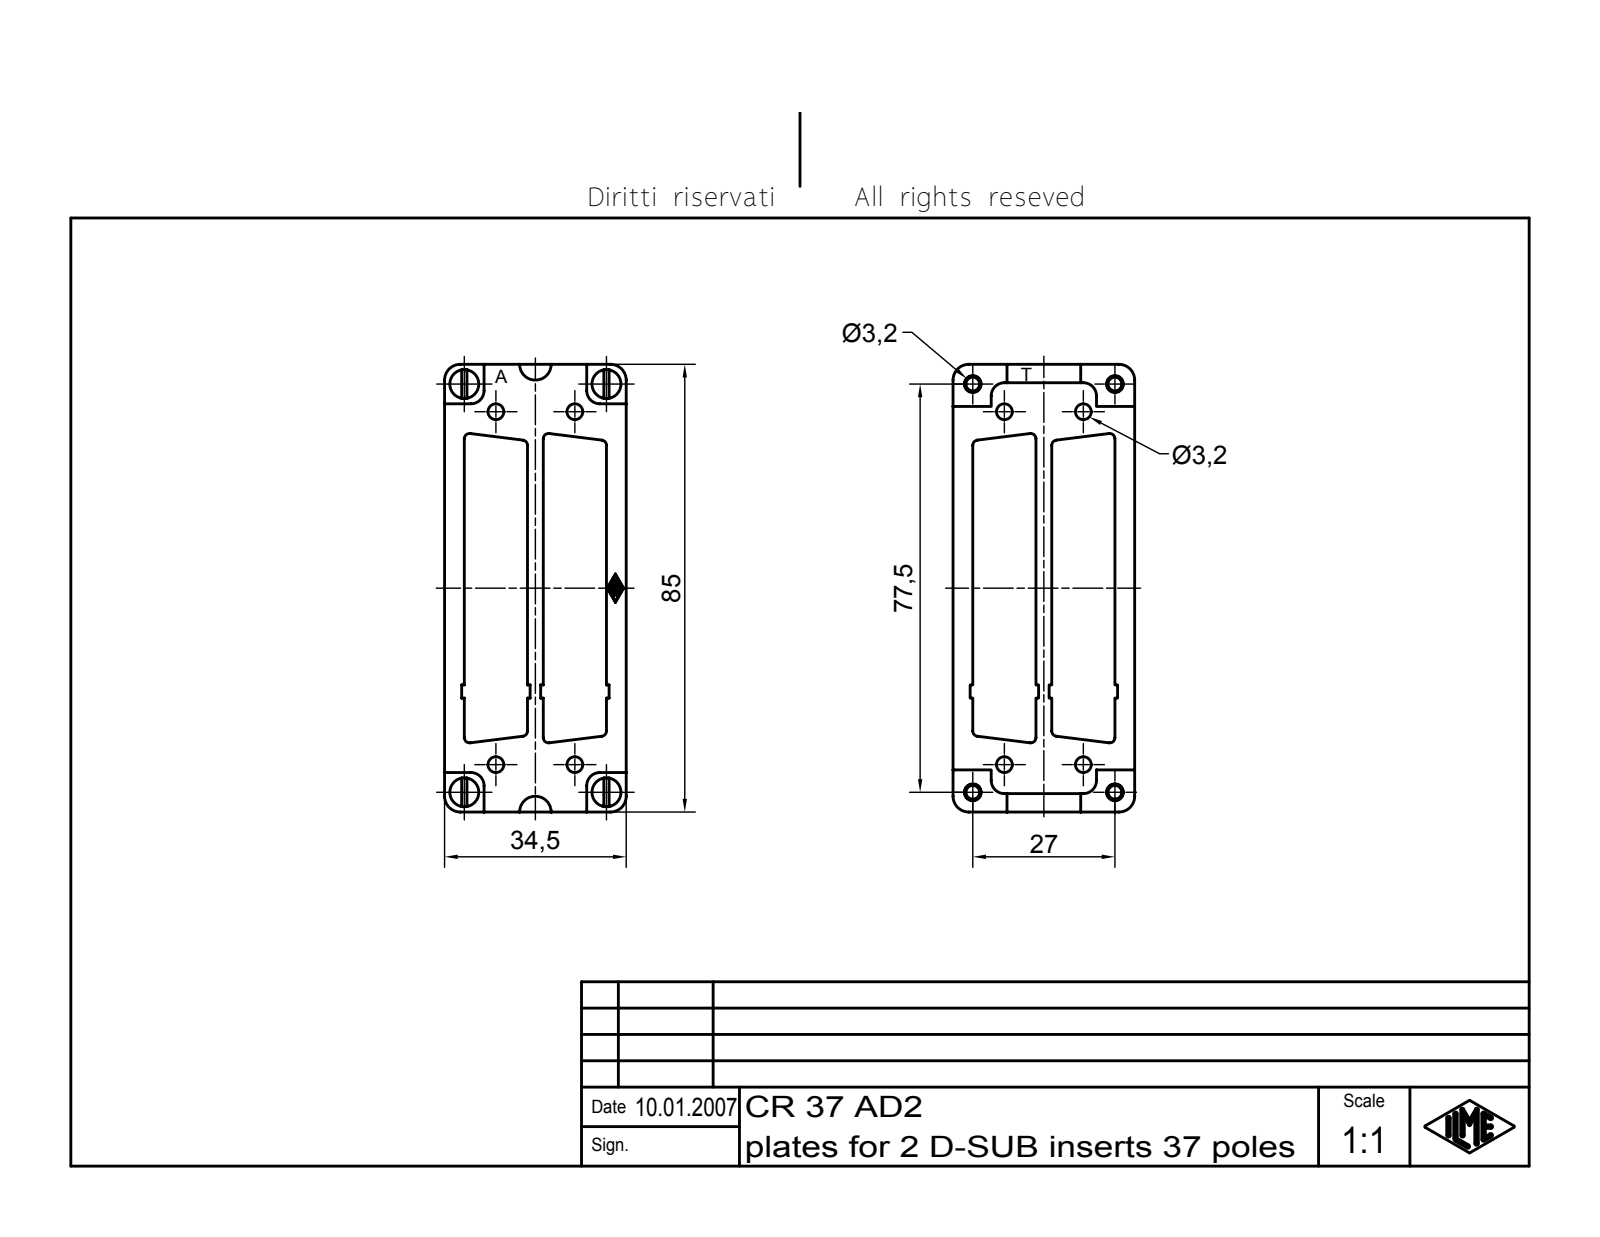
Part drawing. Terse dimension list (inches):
name: CR 37 AD2
written by: Autodesk Inventor 7 (AUTOMOTIVE_DESIGN)
unit: in
bodies: 1 solid, 215 faces (129 planar, 70 cylindrical, 16 other)
size: 3.346 × 1.358 × 0.551
volume: 0.41 in³; area: 10.54 in²
holes: 4× ⌀0.118, 4× ⌀0.126
bosses: 4× ⌀0.217, 4× ⌀0.118
rounds: 14× R0.004, 8× R0.039, 8× R0.098, 6× R0.118
face distances: 0.118, 0.315, 0.148, 0.472, 0.591, 0.62, 0.738, 1.211, 0.276, 1.358
hole spacings: 0.314, 0.852, 2.854, 2.962, 0.591, 1.063, 2.638, 2.703
